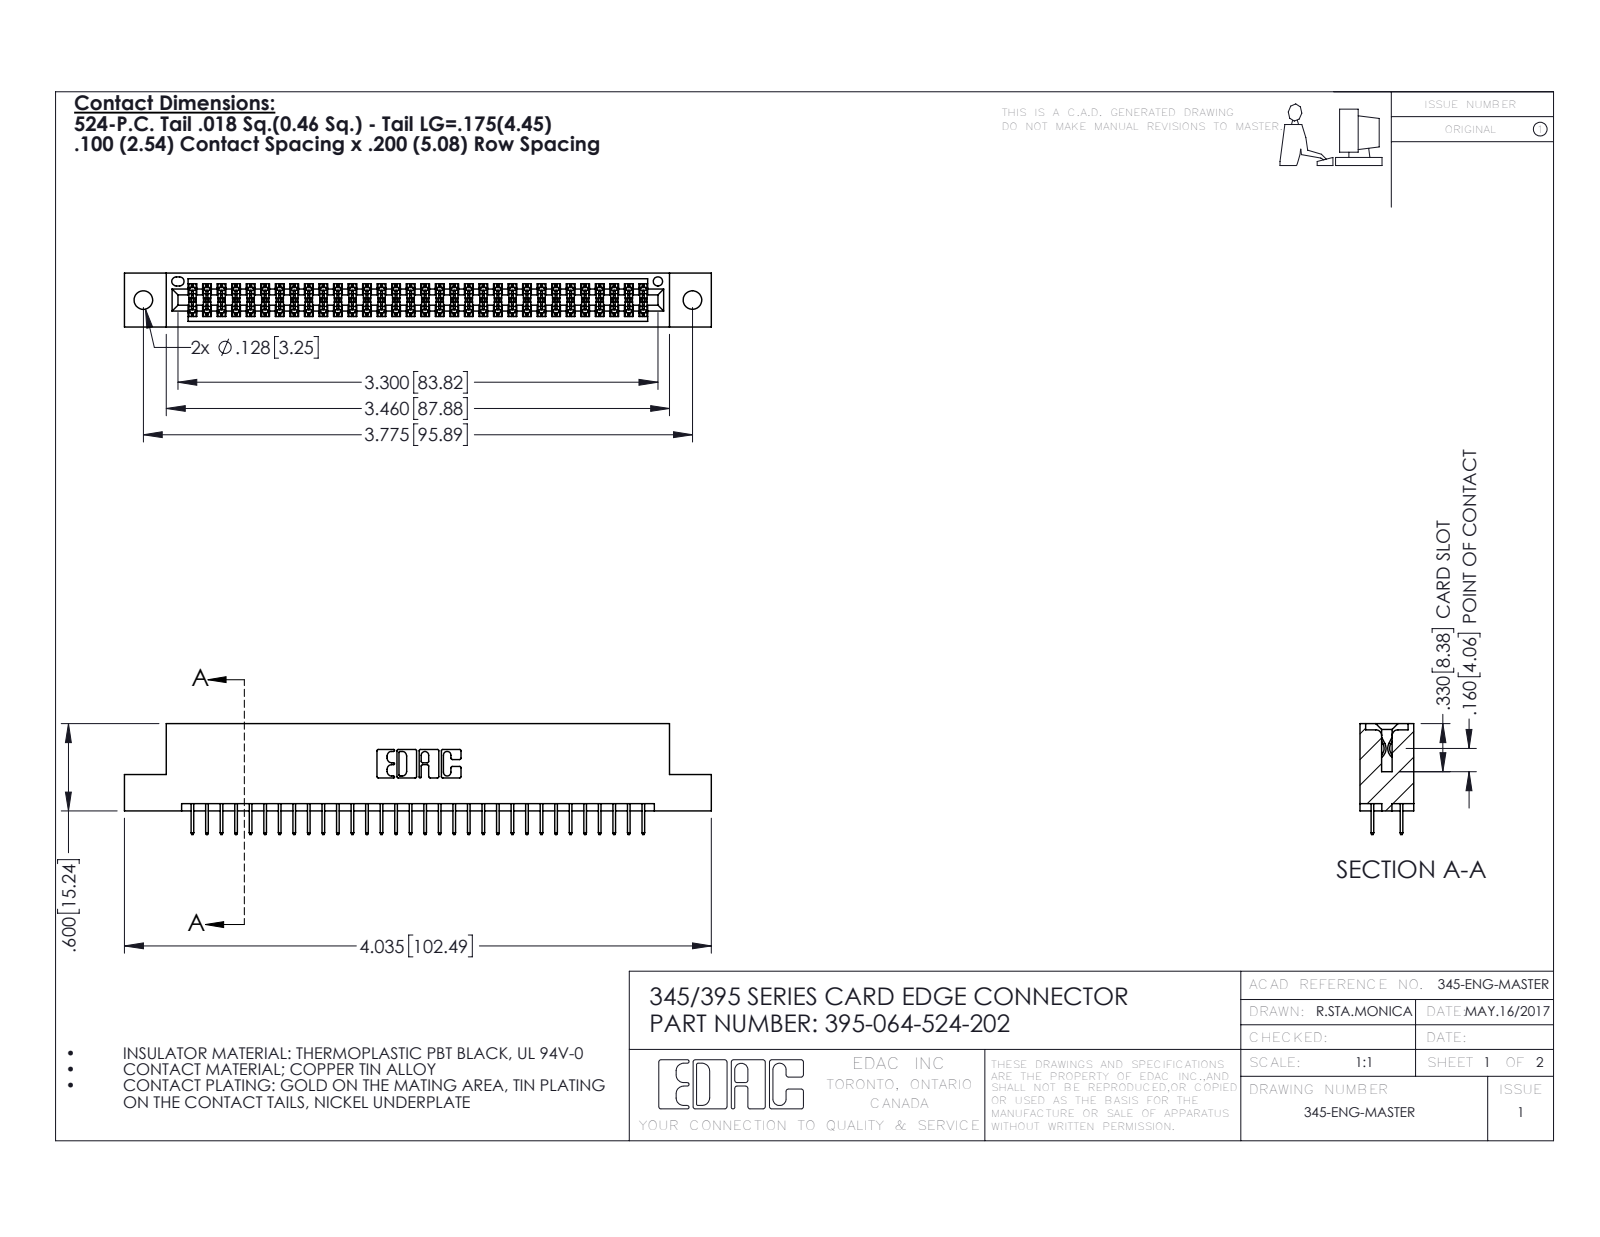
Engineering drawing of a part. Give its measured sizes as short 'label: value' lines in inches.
name: 395-064-524-202; 345-292-001_345-293-124; 345 Part_Flush Mounting Lugs - 0.128 Dia
written by: SolidWorks 2016 (CONFIG_CONTROL_DESIGN)
unit: in
bodies: 65 solids, 3582 faces (2576 planar, 1006 cylindrical, 0 other)
size: 4.035 × 0.762 × 0.37
volume: 0.594 in³; area: 21.17 in²
holes: 2× ⌀0.128, 1× ⌀0.064
rounds: 96× R0.006, 22× R0.01, 6× R0.007, 6× R0.031, 3× R0.026, 2× R0.014, 2× R0.019, 2× R0.022
face distances: 0.298, 0.072, 0.2, 0.37, 0.098, 0.272, 0.025, 0.225, 0.072, 0.175
hole spacings: 0.27, 3.54, 3.775
